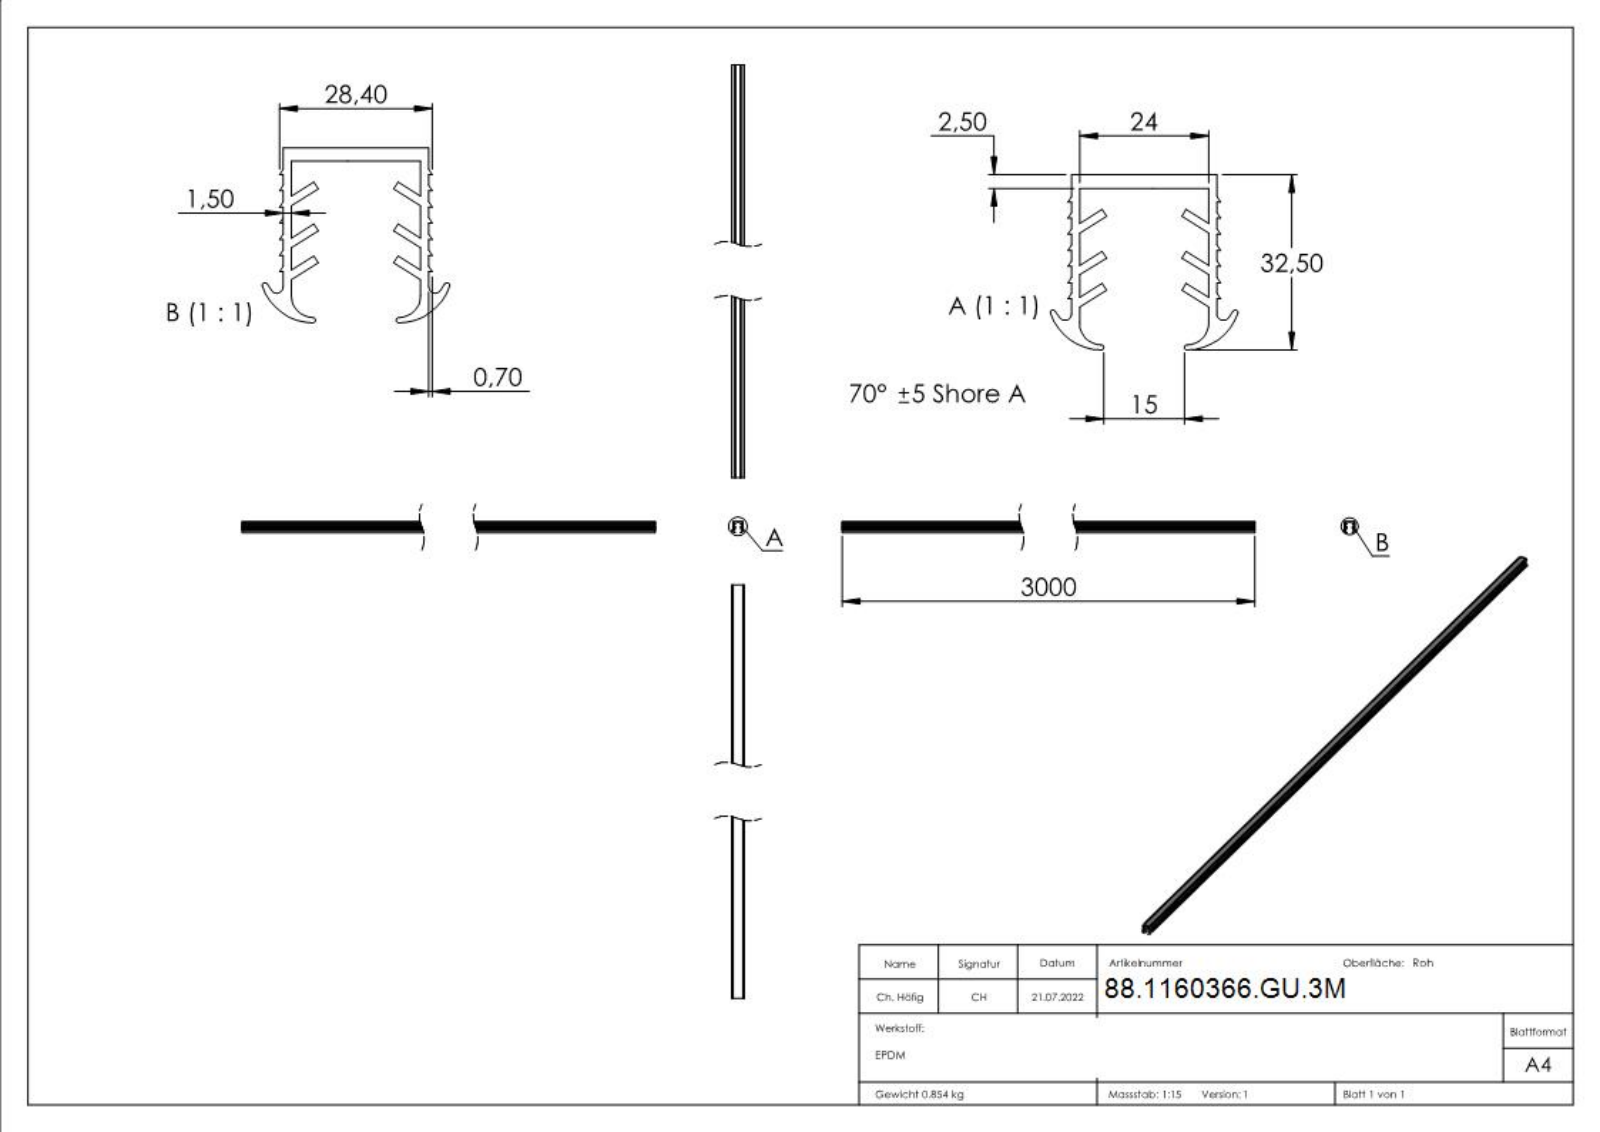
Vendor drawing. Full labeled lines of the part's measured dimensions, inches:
Part name (STEP PRODUCT): 60366-GU-3M
STEP written by: SolidWorks 2018 (CONFIG_CONTROL_DESIGN)
Units: inches
Bodies: 1 solid, 381 faces (223 planar, 10 cylindrical, 148 other)
Overall size (bounding box): 118.11 × 1.371 × 1.28
Volume: 44.15 in³ · Surface area: 1 309 in²
Partial cylindrical surfaces — rounded edges, fillets, slot ends (radius × count): R0.02 ×4, R0.047 ×2, R0.157 ×2, R0.394 ×2
Main face-to-face distances: 0.059, 1.004, 0.098, 0.199, 0.259, 0.459, 0.945, 1.063, 0.068, 0.2
